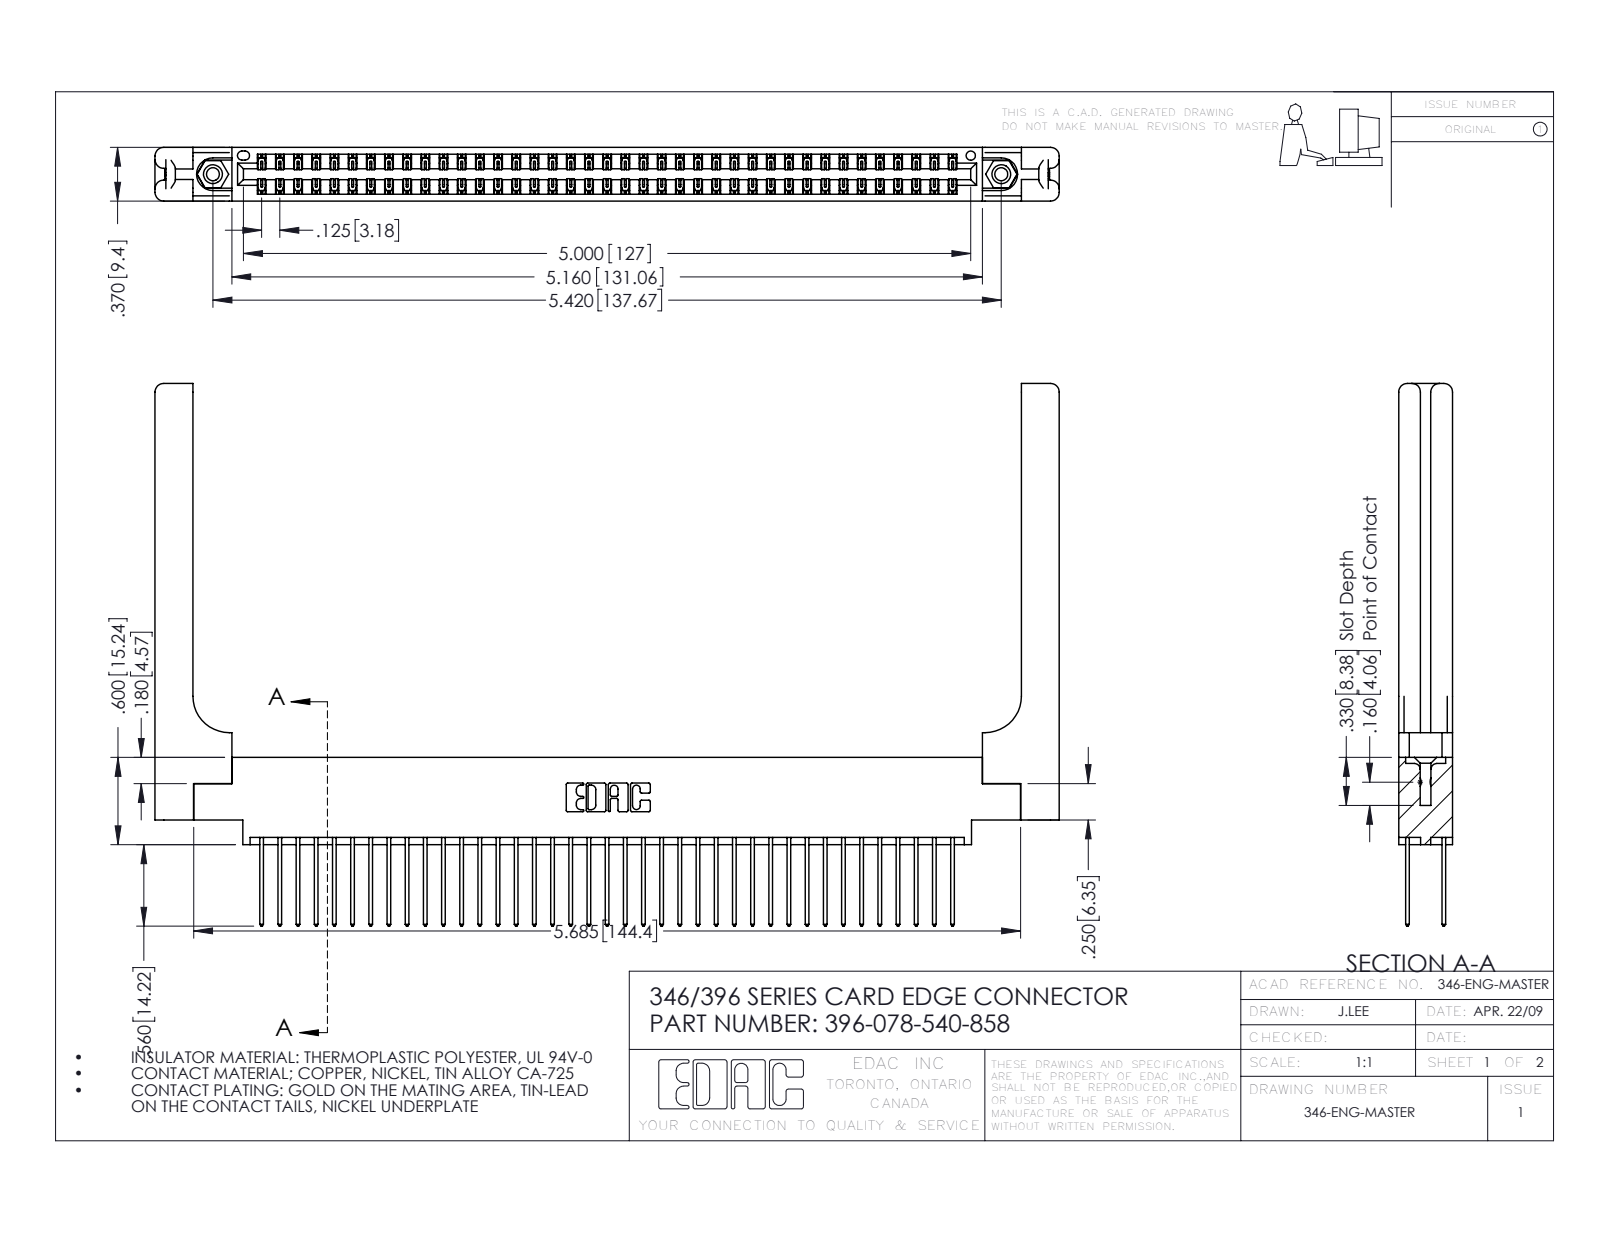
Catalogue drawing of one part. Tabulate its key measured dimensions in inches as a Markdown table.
| quantity | value |
| --- | --- |
| part name | 345-250-001_345-250-001-102; 346-220-058_345-220-058; 396-078-540-858; 345-292-001_345-293-140 (+1 more) |
| STEP written by | SolidWorks 2016 (CONFIG_CONTROL_DESIGN) |
| units | inches |
| bodies | 83 solids, 4438 faces (2958 planar, 1420 cylindrical, 60 other) |
| overall size | 6.216 × 3.73 × 0.37 |
| volume | 1.404 in³ |
| surface area | 43.13 in² |
| round holes (diameter × count) | 0.089 × 2, 0.125 × 2, 0.156 × 2, 0.064 × 1 |
| round bosses / shafts (diameter × count) | 0.155 × 2 |
| partial cylindrical surfaces (radius × count) | 0.006 × 117, 0.01 × 78, 0.01 × 22, 0.06 × 16, 0.007 × 6, 0.031 × 6, 0.026 × 3, 0.014 × 2 |
| main face-to-face distances | 0.048, 0.322, 0.37, 0.072, 0.25, 0.025, 0.298, 0.148, 0.15, 0.275 |
| hole center spacings | 0.246, 5.211, 5.42 |
